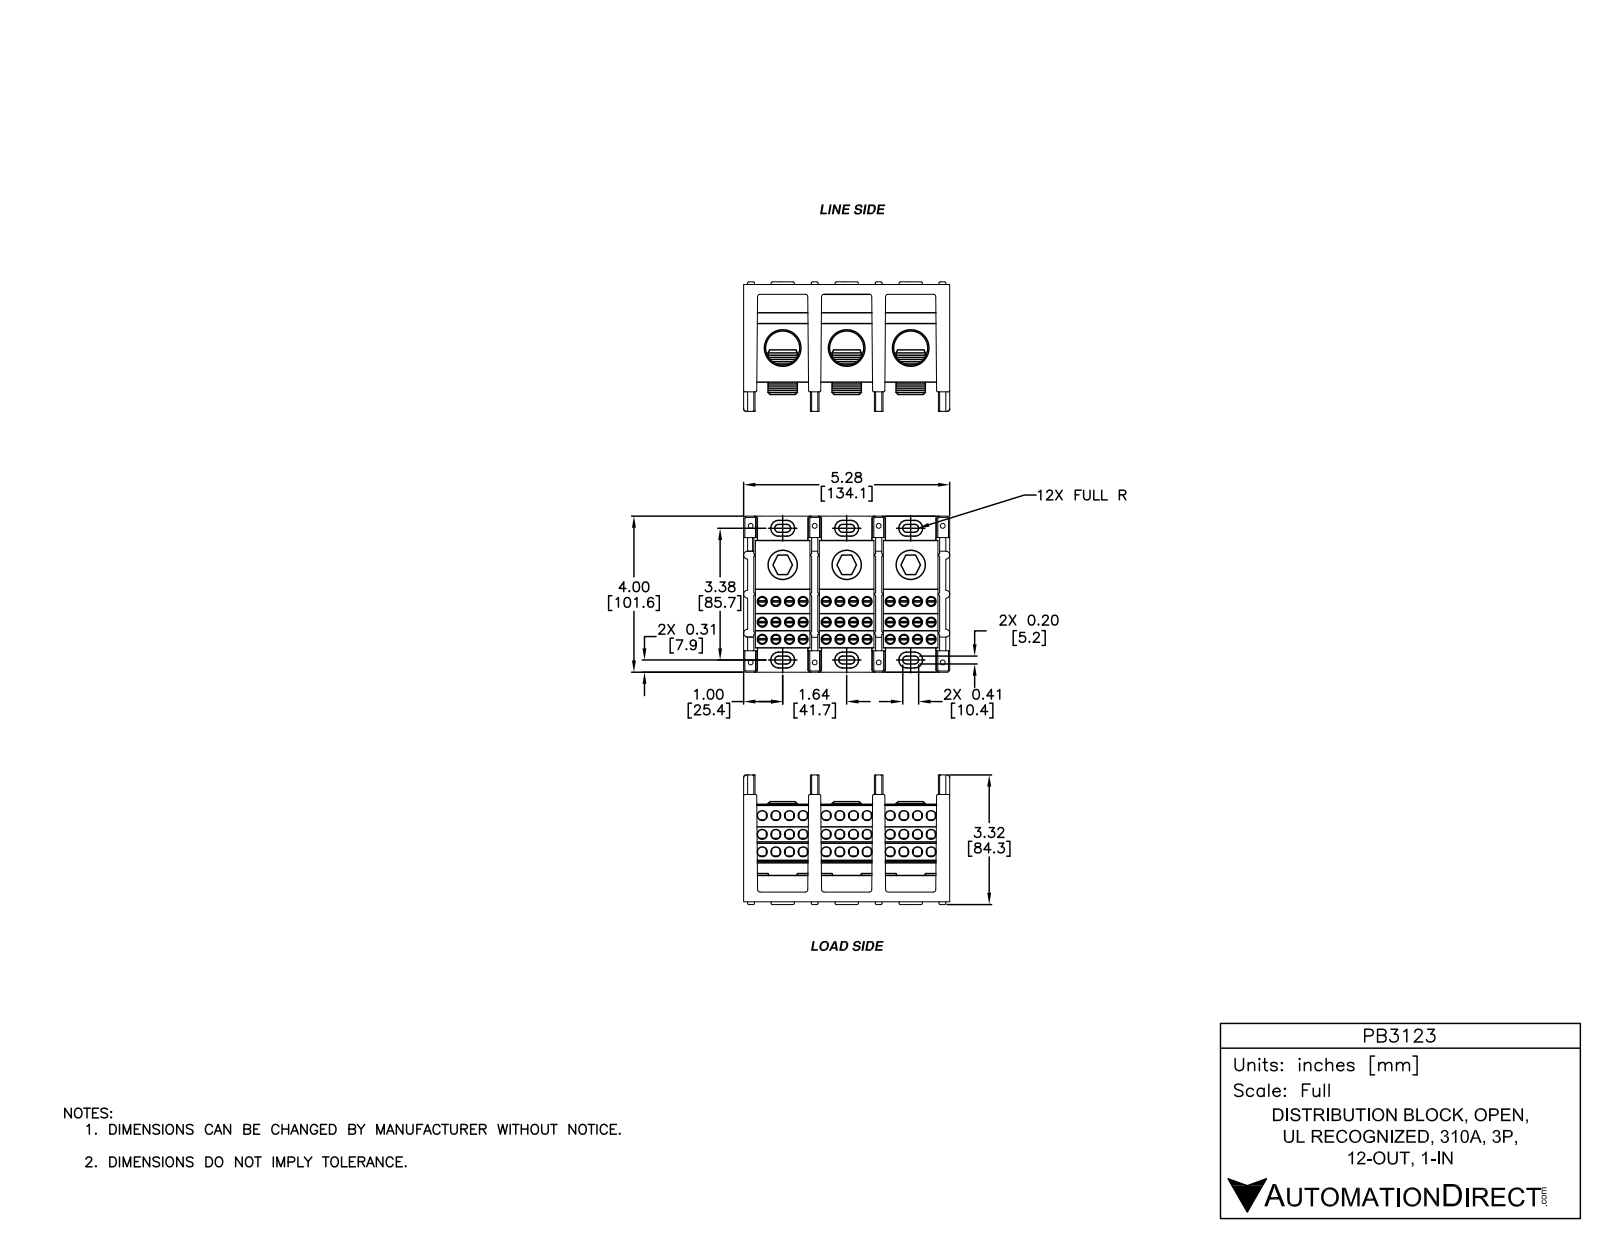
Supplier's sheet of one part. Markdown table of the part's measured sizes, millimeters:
| quantity | value |
| --- | --- |
| part name | PB3123 |
| STEP written by | SolidWorks 2014 (AUTOMOTIVE_DESIGN) |
| units | millimeters |
| bodies | 10 solids, 1762 faces (720 planar, 737 cylindrical, 305 other) |
| overall size | 134.1 × 101.6 × 85.1 |
| volume | 431 300 mm³ |
| surface area | 188 600 mm² |
| round holes (diameter × count) | 5.6 × 60, 6.4 × 36, 3.2 × 8, 19.1 × 4, 12.7 × 3, 22.2 × 3 |
| round bosses / shafts (diameter × count) | 4.4 × 8, 1.6 × 7, 9.5 × 3 |
| partial cylindrical surfaces (radius × count) | 0.8 × 81, 2.5 × 54, 1.6 × 37, 5.2 × 24, 1.6 × 20, 2.4 × 12 |
| main face-to-face distances | 41.7, 83.3, 4, 37.6, 45.7, 2.5, 79.3, 19.1, 8.9, 87.4 |
| hole center spacings | 8.9, 17.8, 8.9, 16.2, 25.2, 26.6, 83.4, 14.2 |
